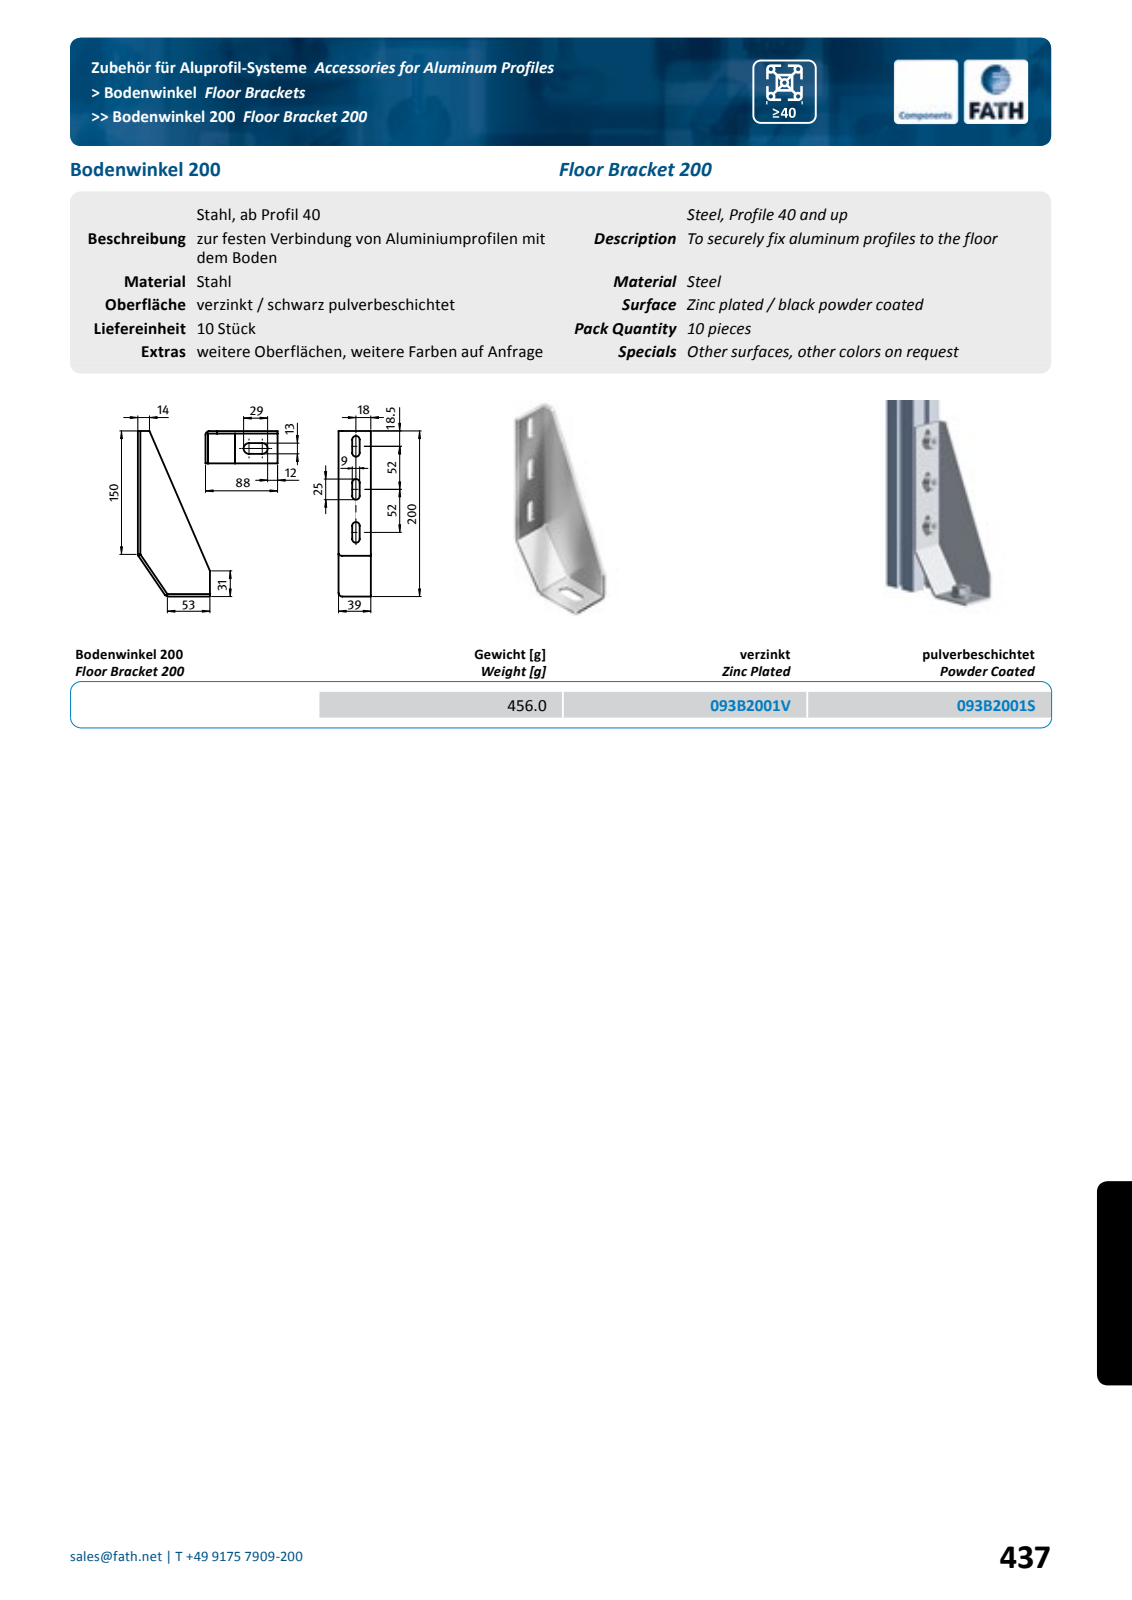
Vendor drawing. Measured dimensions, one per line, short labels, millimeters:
name: fath_093b2001s
written by: Spatial InterOp 3D (automotive_design)
unit: mm
bodies: 1 solid, 128 faces (74 planar, 54 cylindrical, 0 other)
size: 200 × 87 × 39
volume: 55 140 mm³; area: 39 648 mm²
rounds: 16× R1.98, 16× R2, 9× R4.5, 3× R1.5, 2× R6.5
face distances: 3, 39, 36, 13.5, 22.5, 87, 84, 200, 197, 16.5
